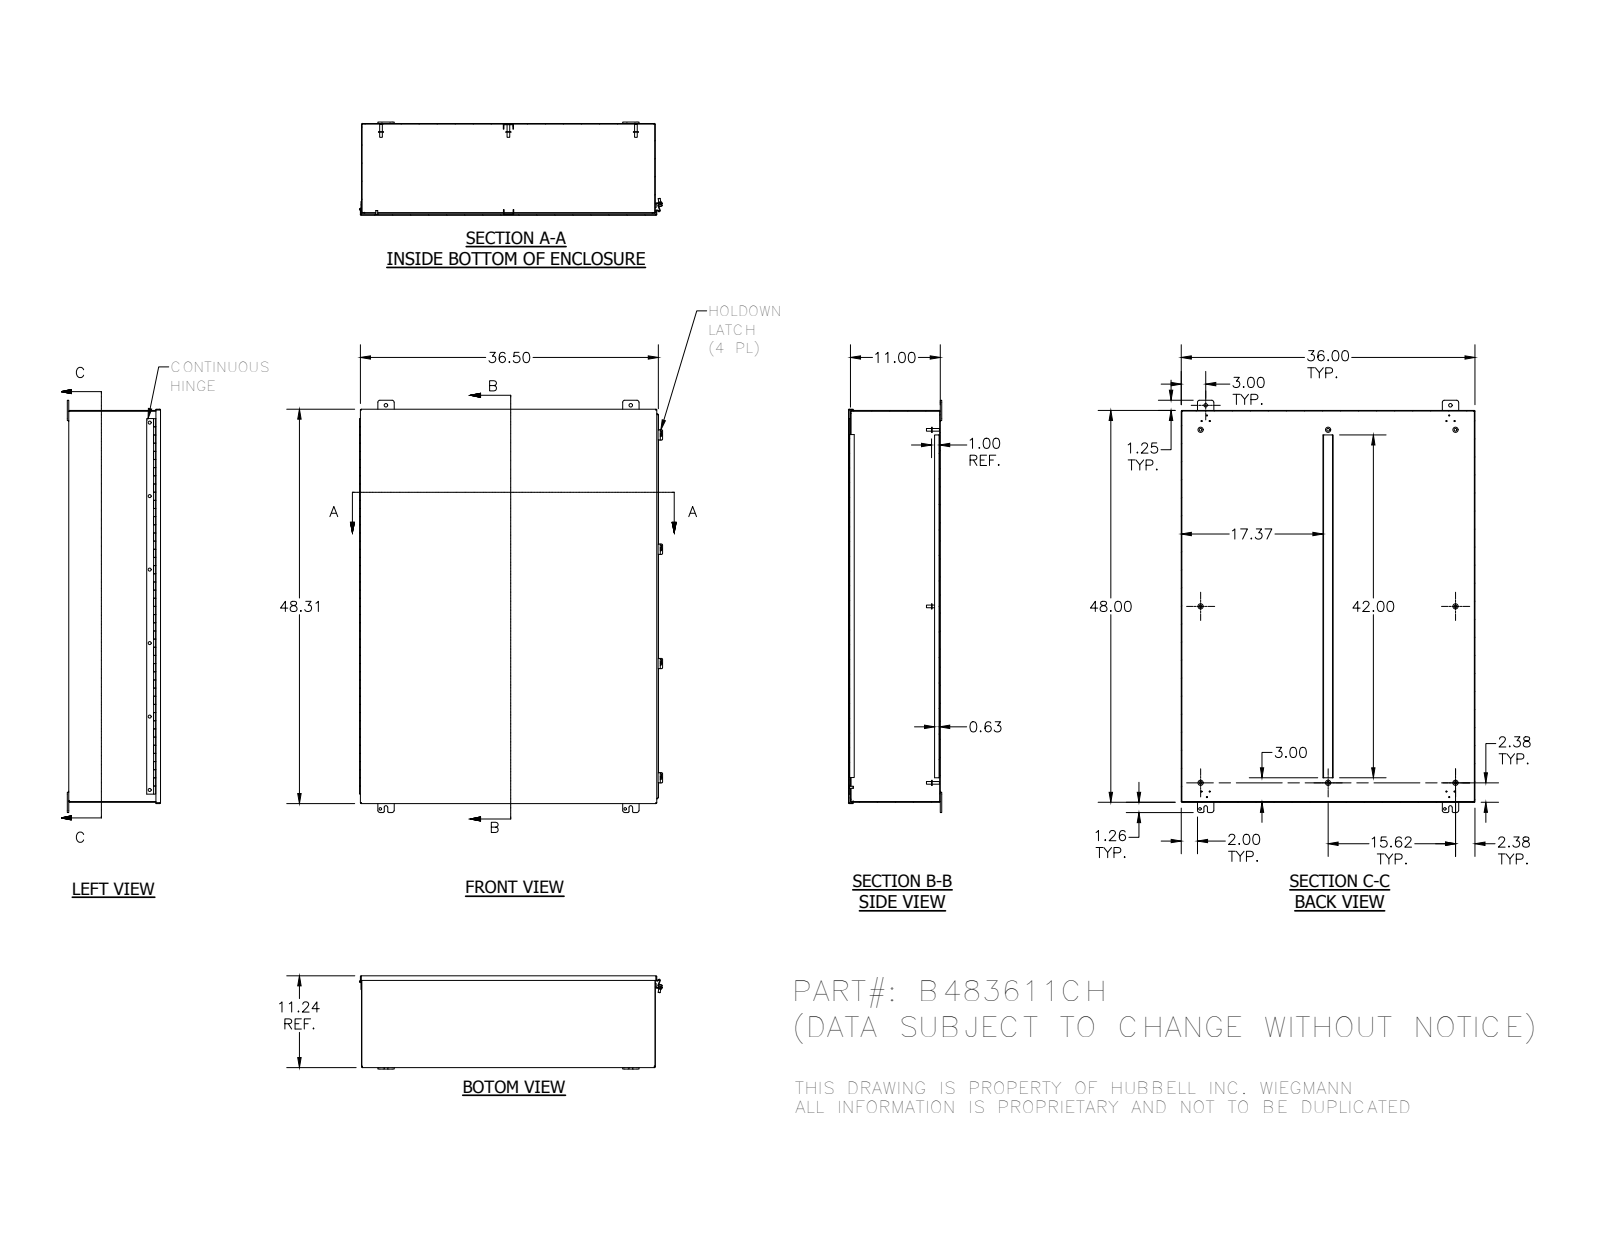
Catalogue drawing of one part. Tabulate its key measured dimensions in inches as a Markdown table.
| quantity | value |
| --- | --- |
| part name | B483611CH; B483611CHBKP; B4836CHLID; H6010109 (+8 more) |
| STEP written by | Autodesk Inventor 2012 (AUTOMOTIVE_DESIGN) |
| units | inches |
| bodies | 32 solids, 1053 faces (663 planar, 303 cylindrical, 87 other) |
| overall size | 50.505 × 37.136 × 11.423 |
| volume | 429.4 in³ |
| surface area | 11 624 in² |
| round holes (diameter × count) | 0.11 × 8, 0.375 × 6, 0.196 × 4, 0.313 × 4, 0.438 × 4, 0.125 × 1, 0.125 × 1 |
| round bosses / shafts (diameter × count) | 0.625 × 8, 0.33 × 8, 0.25 × 6, 0.41 × 4, 0.344 × 4, 0.337 × 1, 0.12 × 1 |
| partial cylindrical surfaces (radius × count) | 0.125 × 24, 0.063 × 16, 0.25 × 16, 0.063 × 11, 0.031 × 8, 0.07 × 8, 0.105 × 8, 0.133 × 8 |
| main face-to-face distances | 0.074, 11.169, 11.095, 11.243, 35.926, 47.926, 36, 35.852, 47.852, 48 |
| hole center spacings | 14, 28, 9, 0.75, 18, 30, 1.593, 13.25 |
